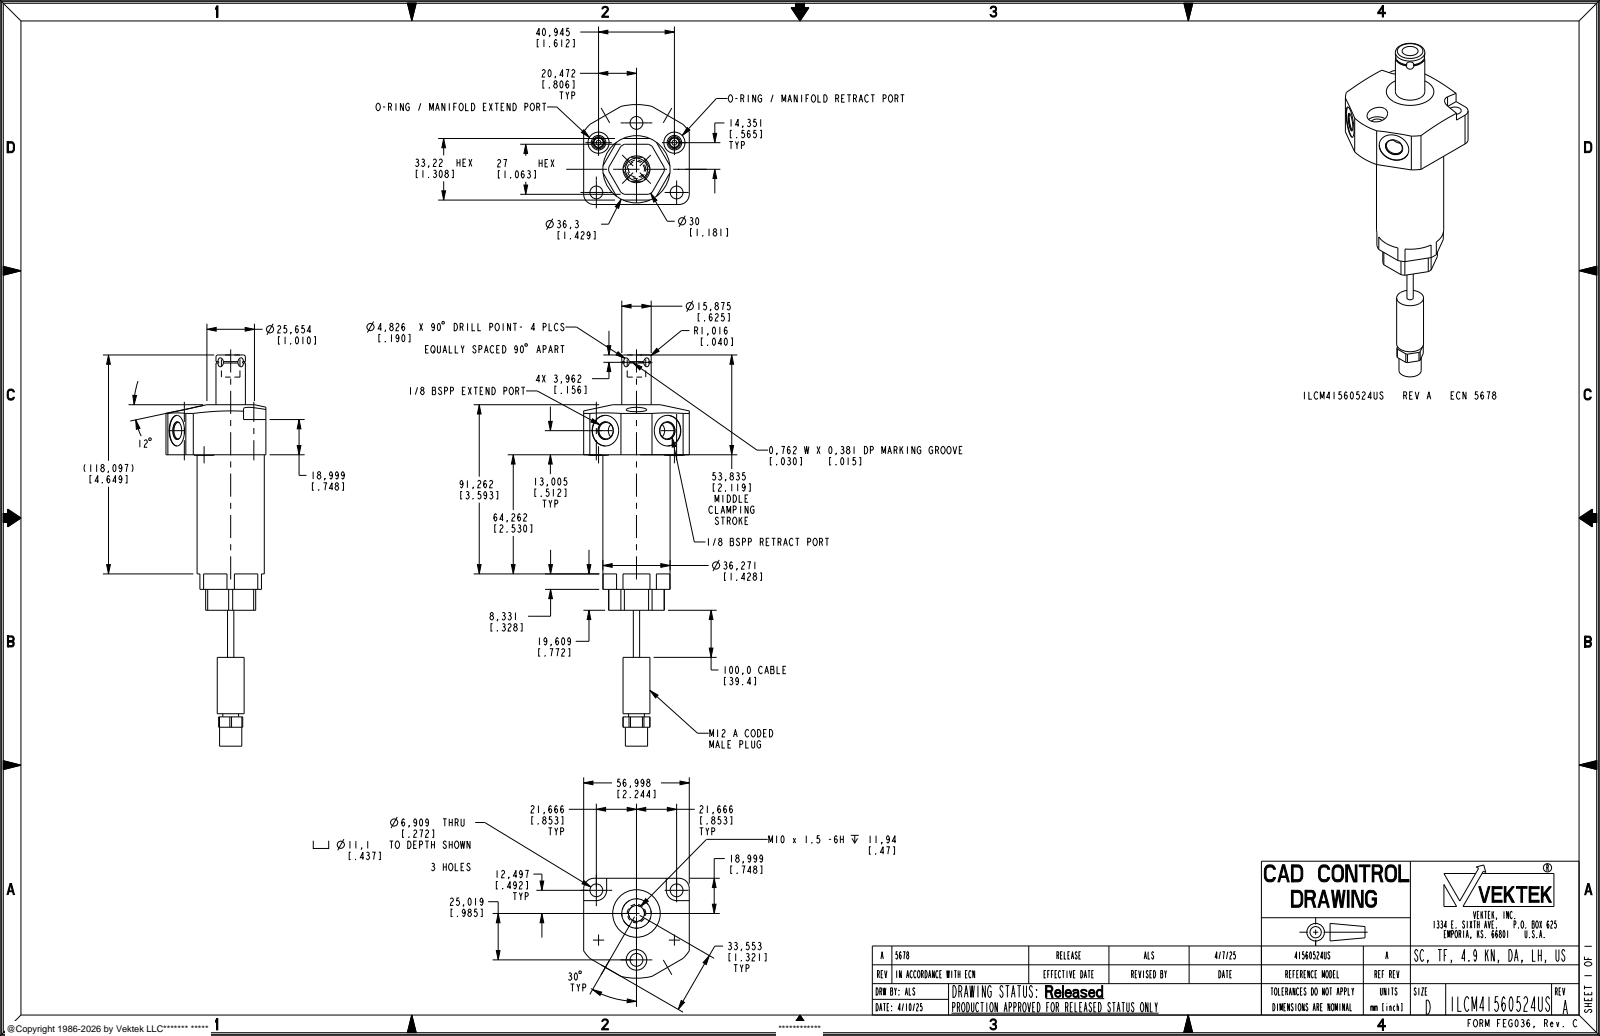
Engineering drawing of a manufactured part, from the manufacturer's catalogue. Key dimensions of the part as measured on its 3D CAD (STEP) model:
Part name (STEP PRODUCT): ILCM41560524US
STEP written by: CREO PARAMETRIC BY PTC INC, 2021164 (AUTOMOTIVE_DESIGN)
Units: millimetres
Bodies: 1 solid, 192 faces (87 planar, 75 cylindrical, 30 other)
Overall size (bounding box): 211.01 × 62.08 × 60.27
Volume: 156 392 mm³ · Surface area: 28 048 mm²
Round holes (diameter × count): ⌀6.91 ×3, ⌀2.49 ×2, ⌀6.5 ×2, ⌀8.84 ×2, ⌀11.4 ×2, ⌀16.51 ×2, ⌀8.61 ×1, ⌀11.1 ×1, ⌀22.73 ×1
Round bosses / shafts (diameter × count): ⌀5.49 ×2, ⌀36.27 ×1, ⌀15.88 ×1, ⌀14.5 ×1, ⌀11.99 ×1, ⌀10.01 ×1, ⌀8.51 ×1, ⌀3.4 ×1
Partial cylindrical surfaces — rounded edges, fillets, slot ends (radius × count): R5.55 ×2, R5.56 ×2, R7.56 ×1, R15 ×1, R34.92 ×1
Main face-to-face distances: 27, 57, 3.11, 30.11, 83.87, 19.61, 64.26, 21.13, 1.52, 62.74
Hole centre spacings: 25.02, 23.08, 25, 26.88, 43.33, 49.97, 40.94, 43.34
